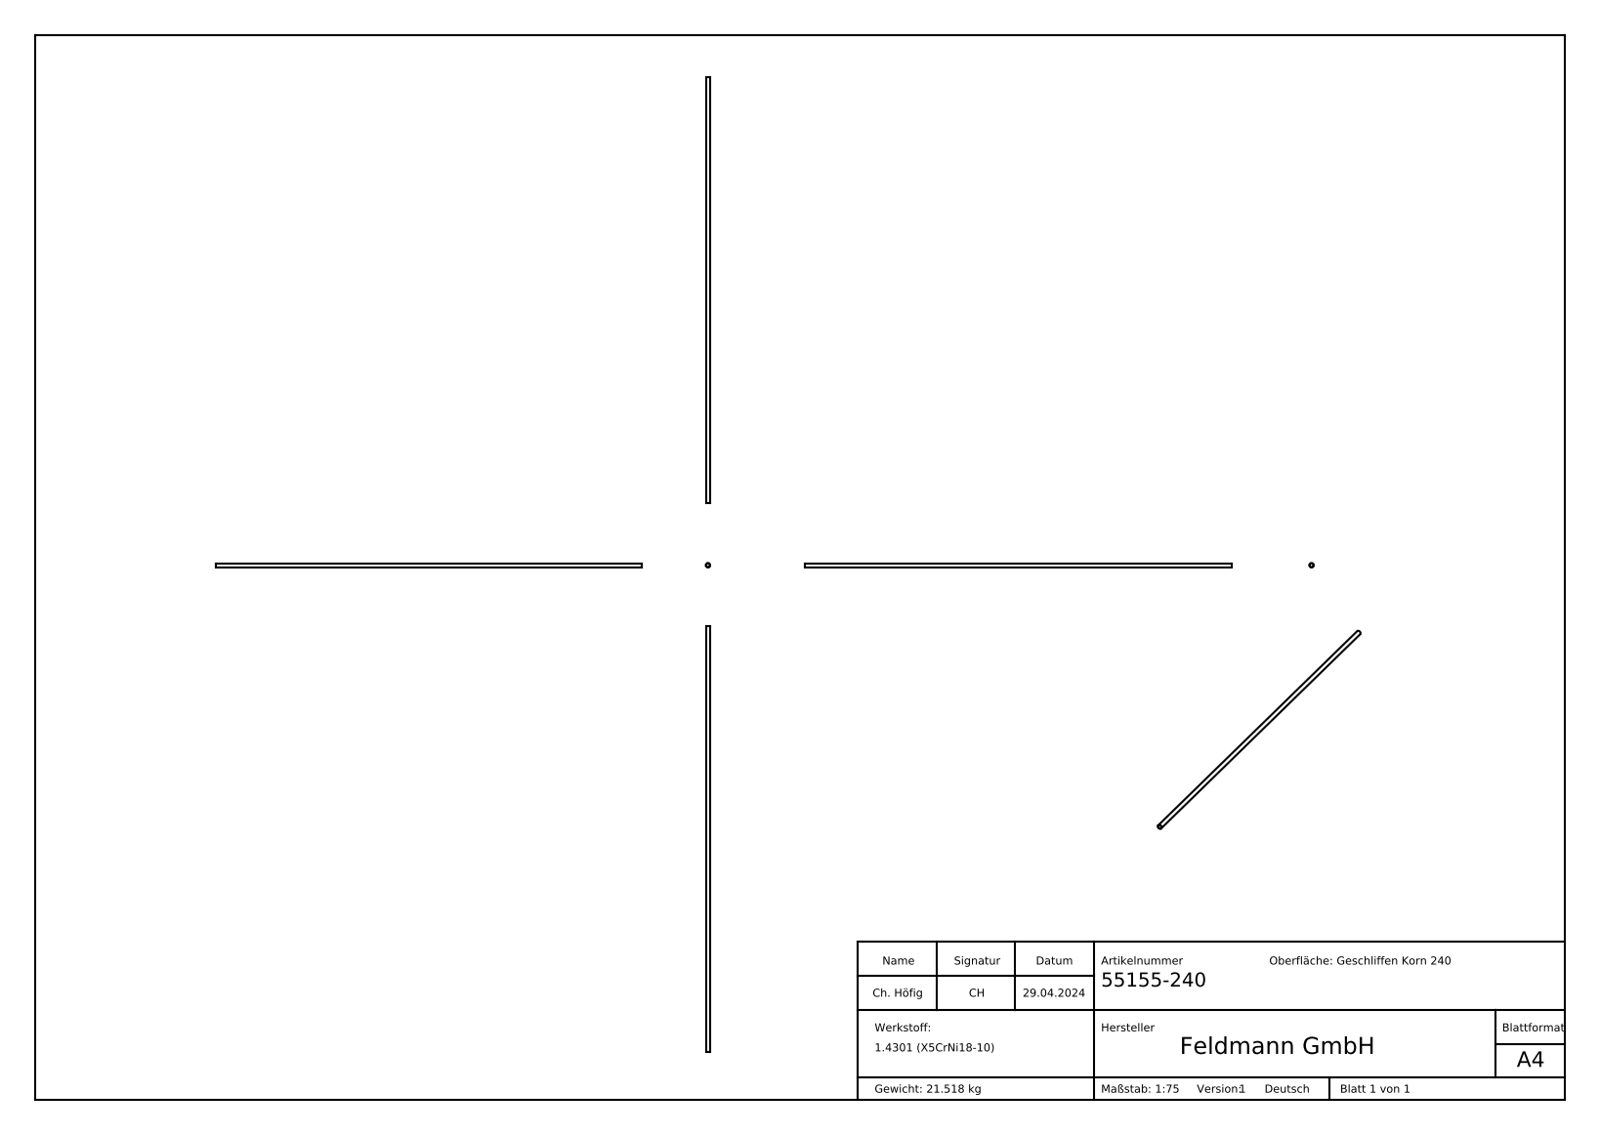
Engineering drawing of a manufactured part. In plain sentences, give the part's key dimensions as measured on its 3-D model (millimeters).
The part is named "55155-240". Its 3-D file was written by "SolidWorks 2018 (CONFIG_CONTROL_DESIGN)". It is 1 solid with 271 faces: 131 planar, 25 cylindrical and 115 other. Overall it measures 6000 by 60.3 by 60.3 millimeters. Its volume is 2 724 000 cubic millimeters and its surface area 2 180 000 square millimeters. Round holes: 1 of diameter 55.3. Round bosses or shafts: 1 of diameter 60.3. Partial cylindrical surfaces (rounded edges, fillets, slot ends): 1 of radius 27.75. The main face-to-face distances are 6000, 2.41, 0.53, 0.73, 0.76, 2.04, 2.61, 2.24, 0.6, 0.79.
